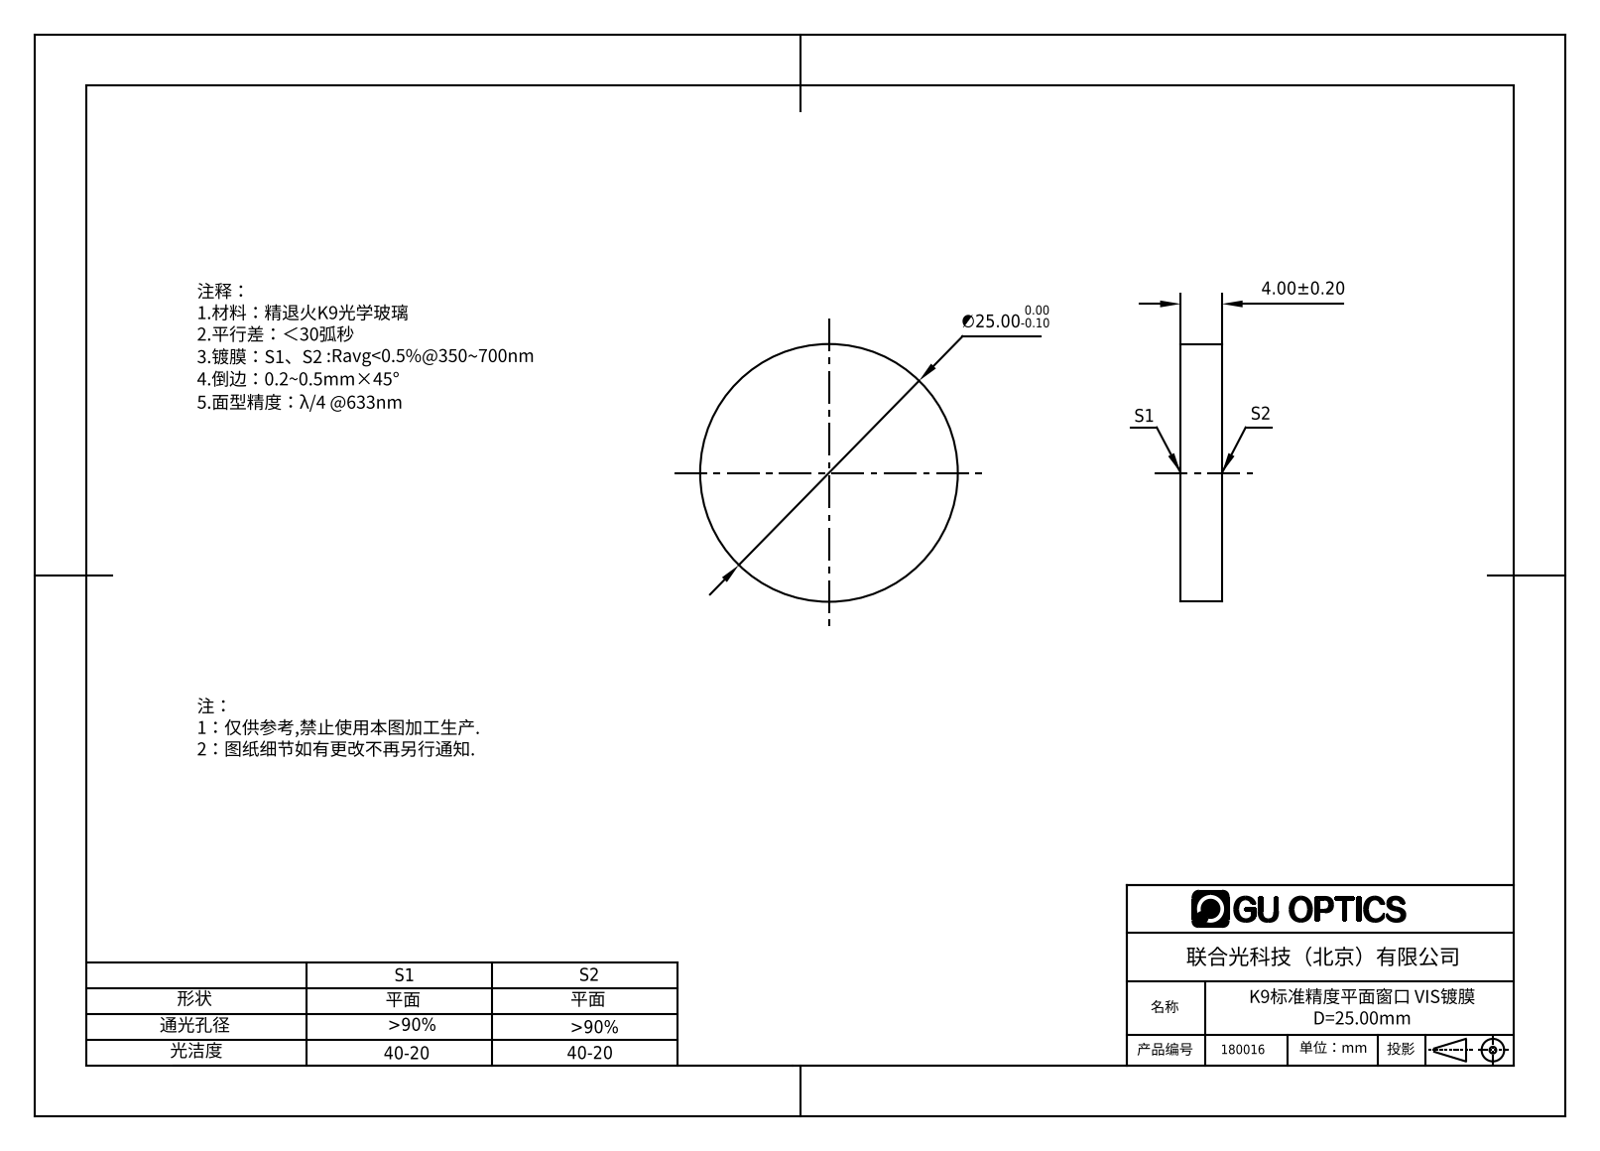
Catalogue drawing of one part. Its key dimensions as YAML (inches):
part_name: "180005"
step_written_by: "SolidWorks 2016 (AUTOMOTIVE_DESIGN)"
units: inches
bodies: {solids: 1, faces: 4, planar: 2, cylindrical: 2, other: 0}
overall_size: [0.984, 0.984, 0.157]
volume: 0.12
surface_area: 2.009
round_bosses_or_shafts:
  - {diameter: 0.984, count: 1}
face_to_face_distances: [0.157]
